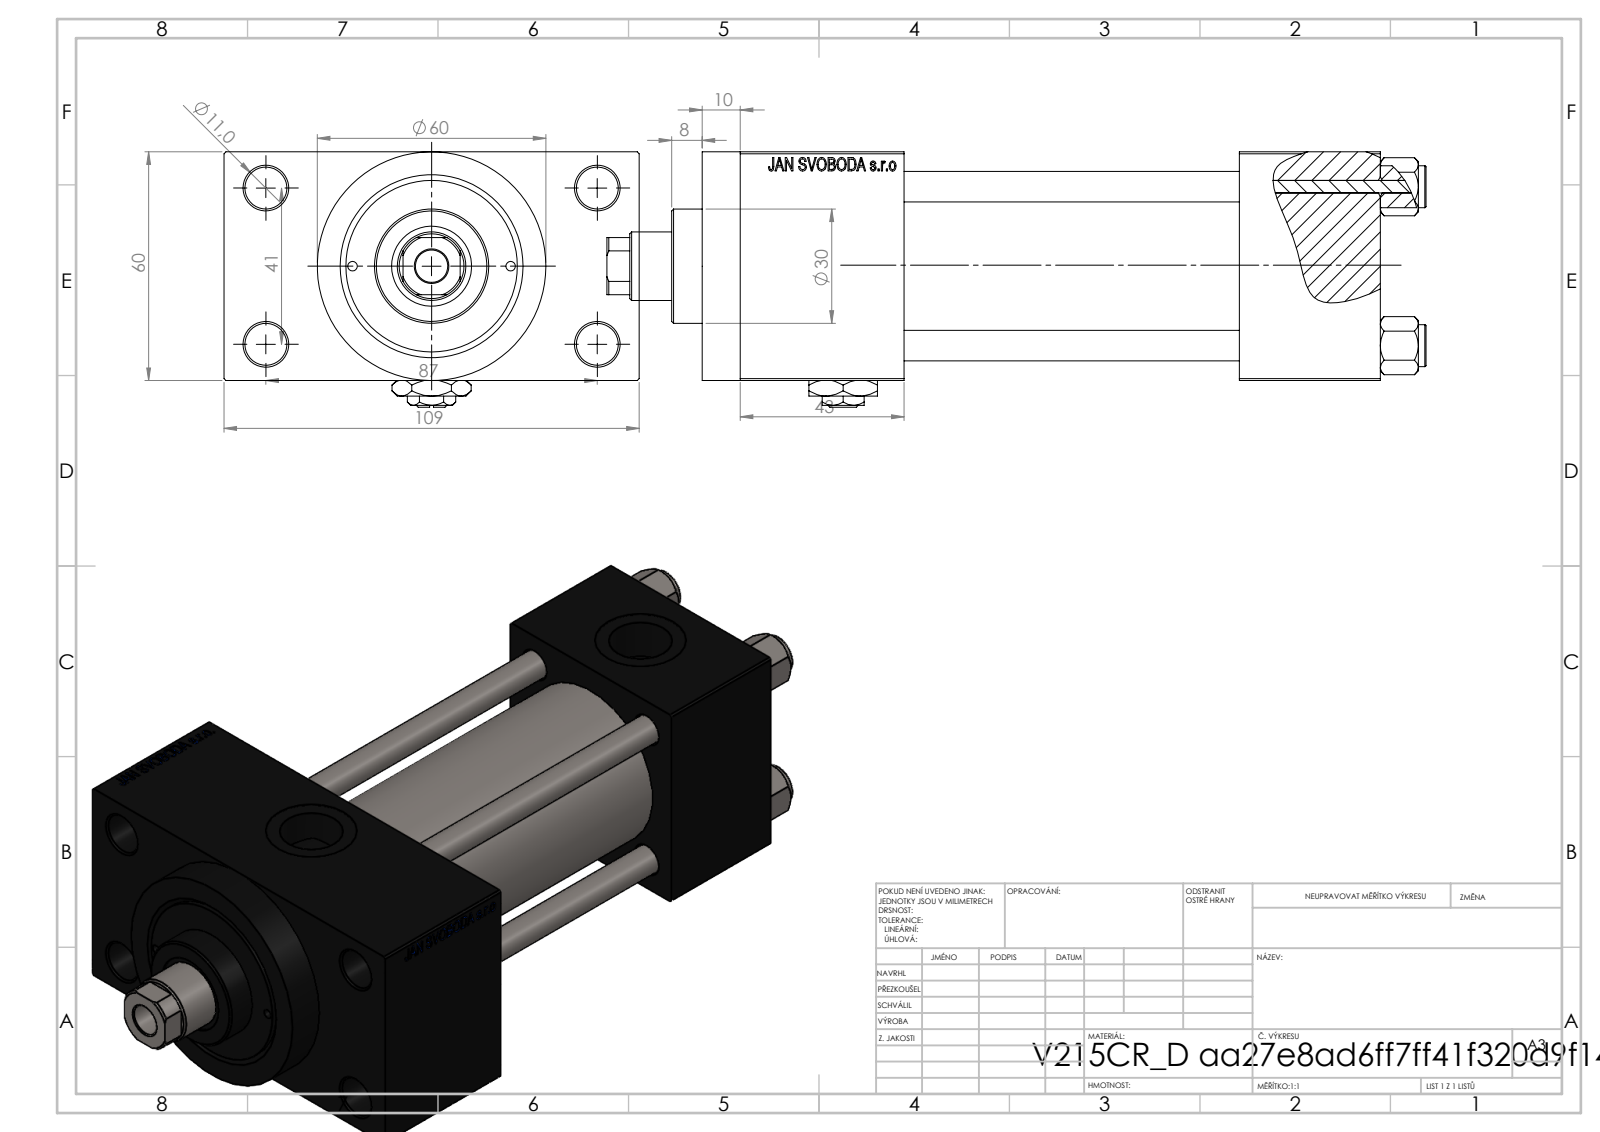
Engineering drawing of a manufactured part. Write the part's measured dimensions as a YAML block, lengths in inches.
part_name: "Zatka_pro_OIL_PORT; V215CR_D_TYCINKA; V215_VC_A; NUT_M5_D (+2 more)"
step_written_by: "SolidWorks 2019 (CONFIG_CONTROL_DESIGN)"
units: inches
bodies: {solids: 12, faces: 1161, planar: 524, cylindrical: 97, other: 540}
overall_size: [8.465, 4.291, 2.638]
volume: 33.13
surface_area: 209.2
round_holes:
  - {diameter: 0.315, count: 4}
  - {diameter: 0.433, count: 4}
  - {diameter: 0.098, count: 2}
  - {diameter: 0.276, count: 2}
  - {diameter: 0.656, count: 2}
  - {diameter: 0.945, count: 2}
  - {diameter: 0.335, count: 1}
  - {diameter: 0.709, count: 1}
  - {diameter: 0.827, count: 1}
  - {diameter: 1.22, count: 1}
  - {diameter: 1.575, count: 1}
  - {diameter: 1.772, count: 1}
round_bosses_or_shafts:
  - {diameter: 0.433, count: 4}
  - {diameter: 2.362, count: 1}
  - {diameter: 1.811, count: 1}
  - {diameter: 1.181, count: 1}
partial_cylinders:
  - {radius: 0.335, count: 1}
face_to_face_distances: [2.362, 0.965, 3.327, 3.465, 1.457, 4.921, 1.693, 6.614, 5.157, 4.291]
hole_center_spacings: [0.821, 0.892, 1.161, 1.206, 1.642, 1.832, 1.856, 1.893]
